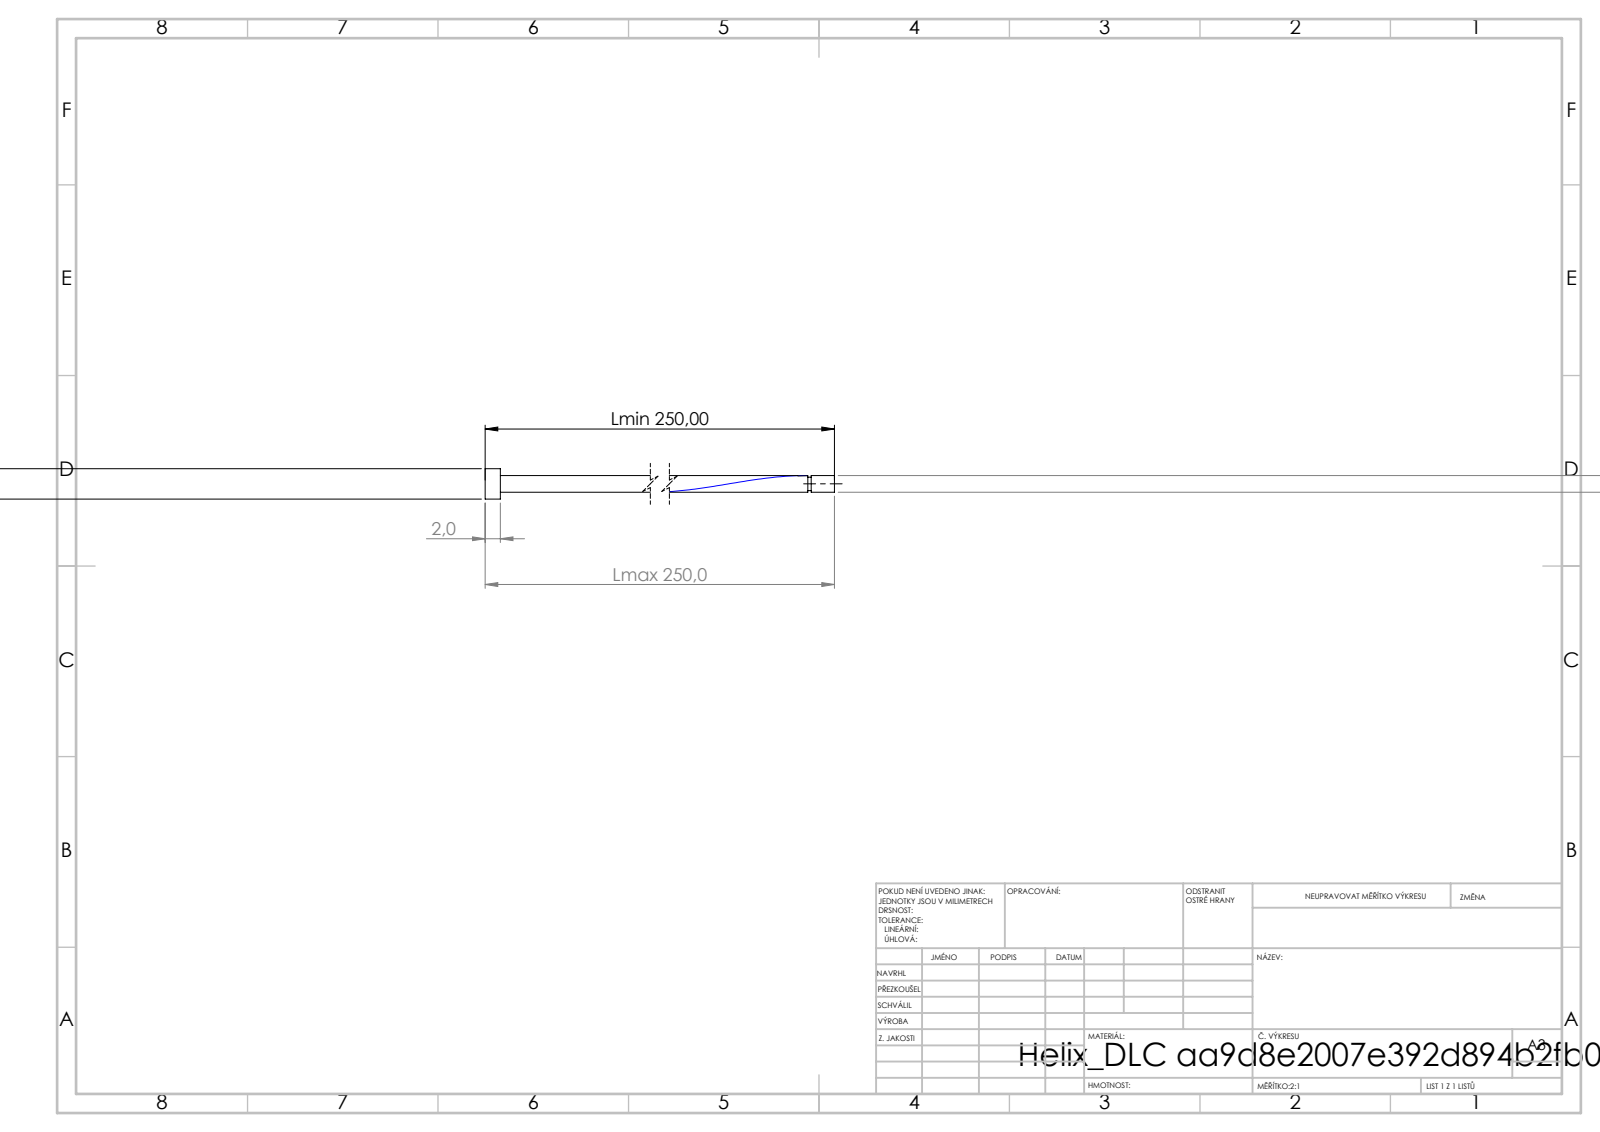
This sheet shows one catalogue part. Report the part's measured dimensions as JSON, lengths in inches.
{"step_written_by": "SolidWorks 2019 (CONFIG_CONTROL_DESIGN)", "units": "inches", "bodies": {"solids": 1, "faces": 16, "planar": 6, "cylindrical": 9, "other": 1}, "overall_size": [9.843, 0.157, 0.157], "volume_in3": 0.071, "surface_area_in2": 3.672, "round_bosses_or_shafts": [[0.157, 1], [0.087, 1], [0.069, 1]], "face_to_face_distances": [0.079, 9.843, 9.764, 9.722, 9.644, 0.12, 9.705, 9.626, 0.017, 0.137]}
